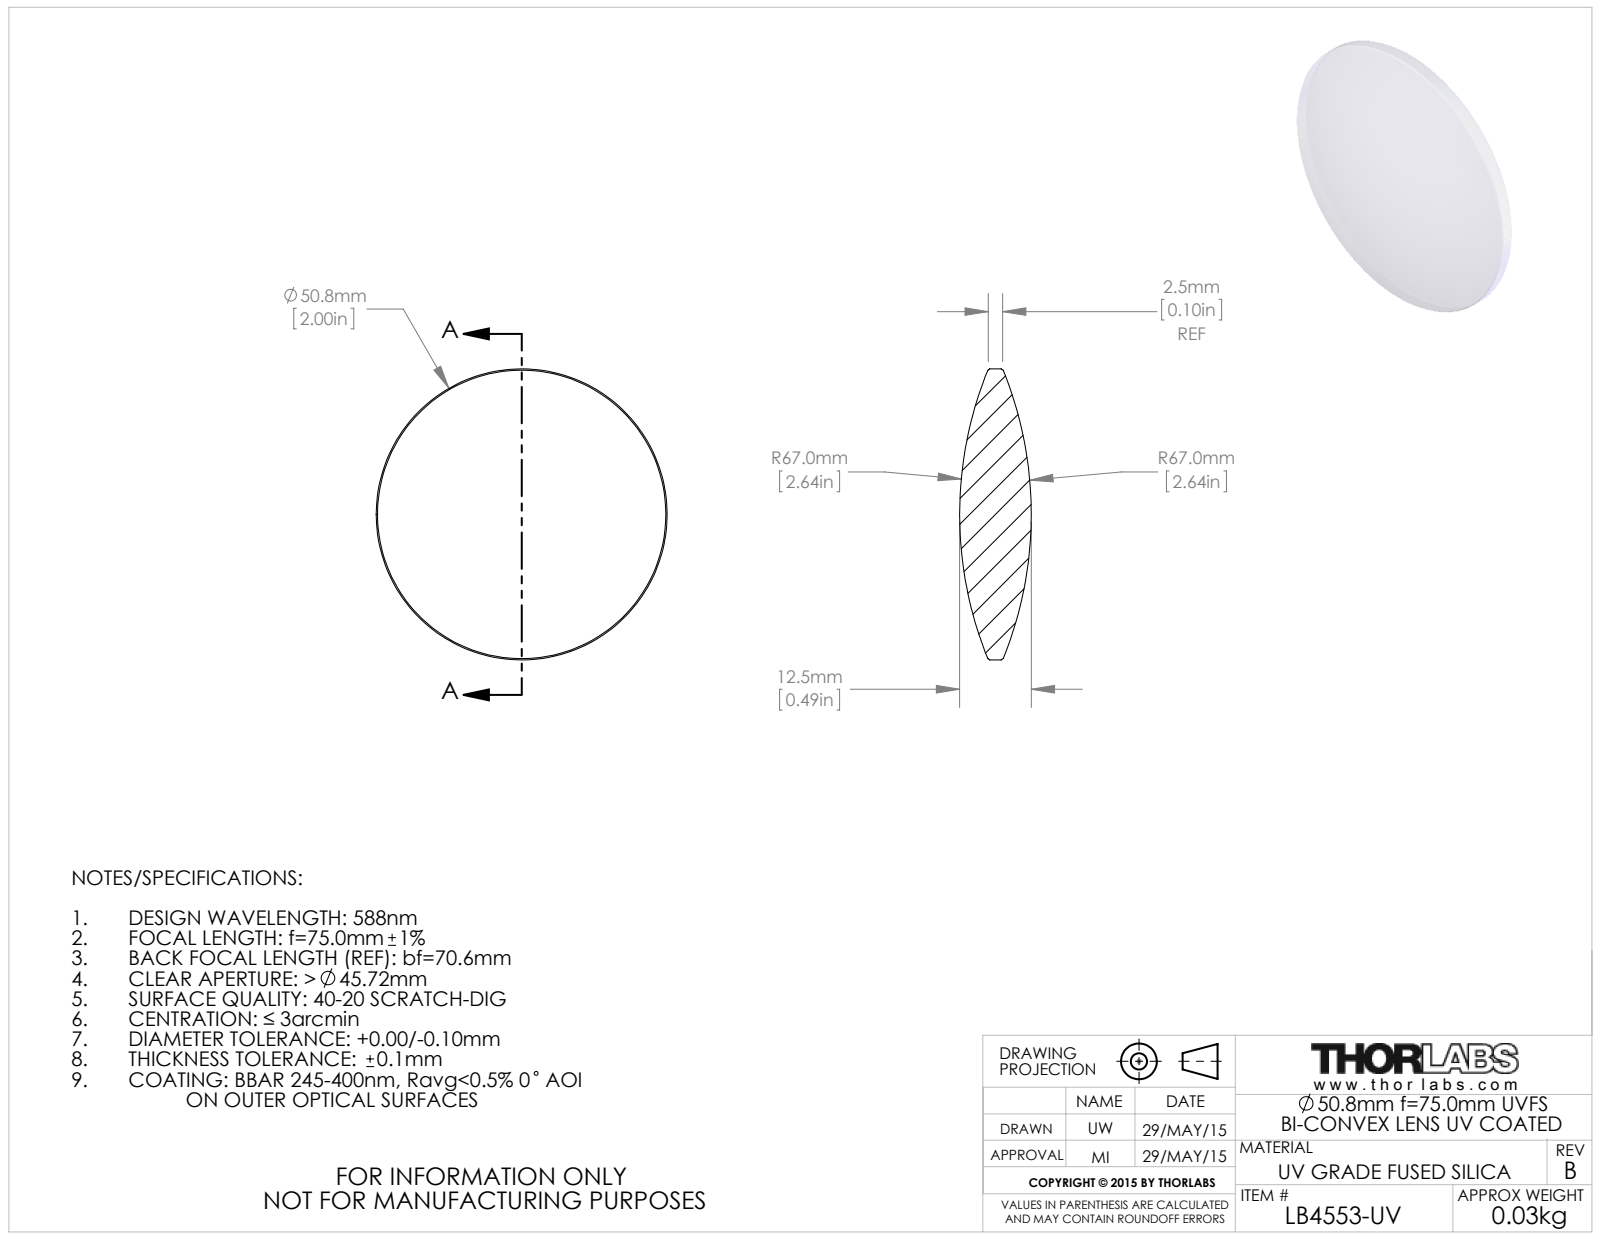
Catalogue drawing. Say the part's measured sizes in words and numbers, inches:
The part is named "4332-E0W". Its 3-D file was written by "SolidWorks 2014 (CONFIG_CONTROL_DESIGN)". It is 1 solid with 10 faces: 0 planar, 2 cylindrical and 8 other. Overall it measures 2 by 2 by 0.492 inches. Its volume is 0.935 cubic inches and its surface area 7.102 square inches. Round bosses or shafts: 1 of diameter 2.
